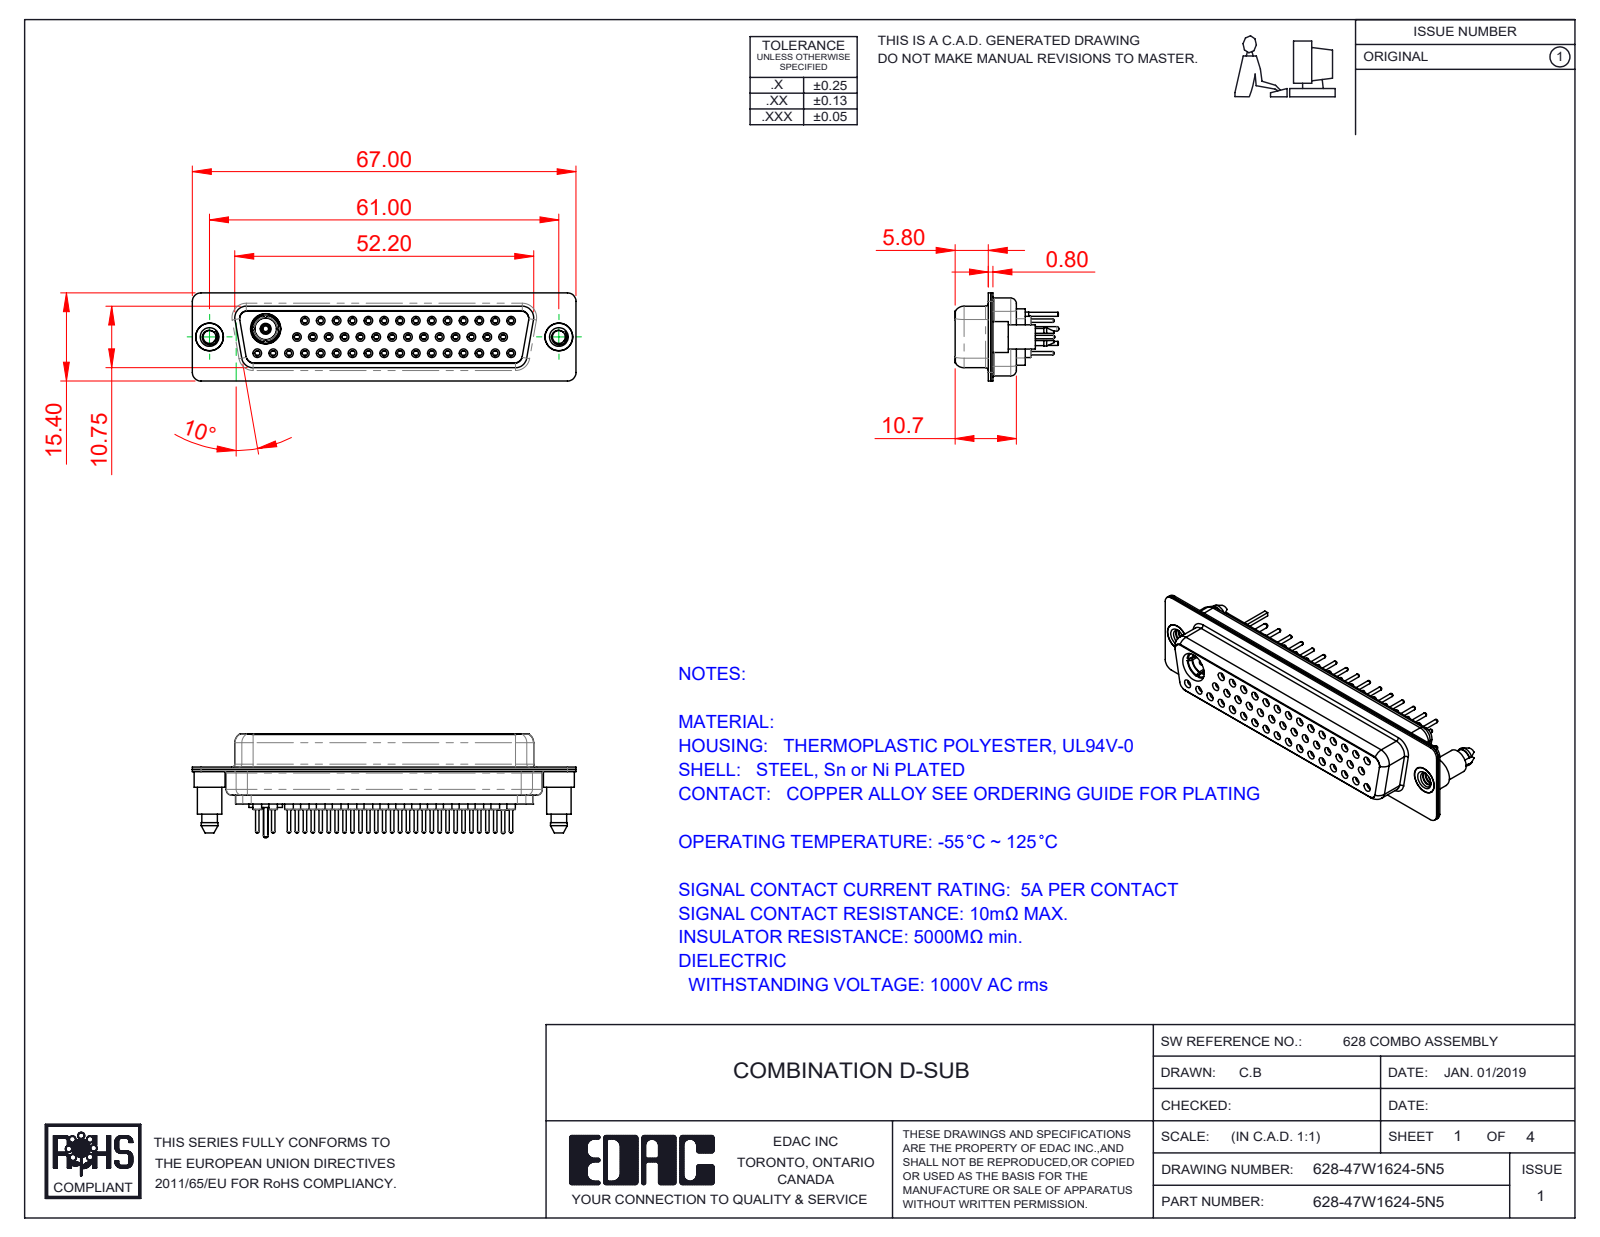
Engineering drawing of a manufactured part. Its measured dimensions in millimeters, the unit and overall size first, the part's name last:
Units: millimetres
Overall size (bounding box): 67 × 18.15 × 15.4
Round holes (diameter × count): ⌀1.1 ×47, ⌀1.5 ×46, ⌀0.9 ×45, ⌀2 ×45, ⌀1.6 ×31, ⌀1.7 ×14, ⌀4.85 ×3, ⌀2.26 ×2, ⌀4 ×2, ⌀4.05 ×2, ⌀2.83 ×1, ⌀3.3 ×1
Round bosses / shafts (diameter × count): ⌀2.2 ×46, ⌀0.6 ×46, ⌀1.6 ×15, ⌀5.4 ×2, ⌀4.95 ×2, ⌀4.8 ×2, ⌀4.25 ×2, ⌀5.85 ×1
Partial cylindrical surfaces — rounded edges, fillets, slot ends (radius × count): R1.5 ×18, R1.35 ×12, R2 ×12, R1.6 ×10, R0.25 ×4, R0.5 ×4, R0.6 ×4, R0.65 ×4
Main face-to-face distances: 0.4, 6.05, 6.45, 11.33, 1.87, 12.25, 6.2, 5.8, 10.35, 10.93
Hole centre spacings: 3.16, 2.77, 5.54, 8.31, 11.08, 13.85, 16.62, 19.39
Volume: 7 178 mm³ · Surface area: 15 213 mm²
Bodies: 55 solids, 2973 faces (827 planar, 1080 cylindrical, 1066 other)
Part name (STEP PRODUCT): 628Combo Threaded Boardlock_5; 628Combo Contact Row 3_24; 628Combo Shell Rear_50 Contacts; Co-Ax Plug Assy_St (+8 more)
STEP written by: SolidWorks 2016 (CONFIG_CONTROL_DESIGN)
